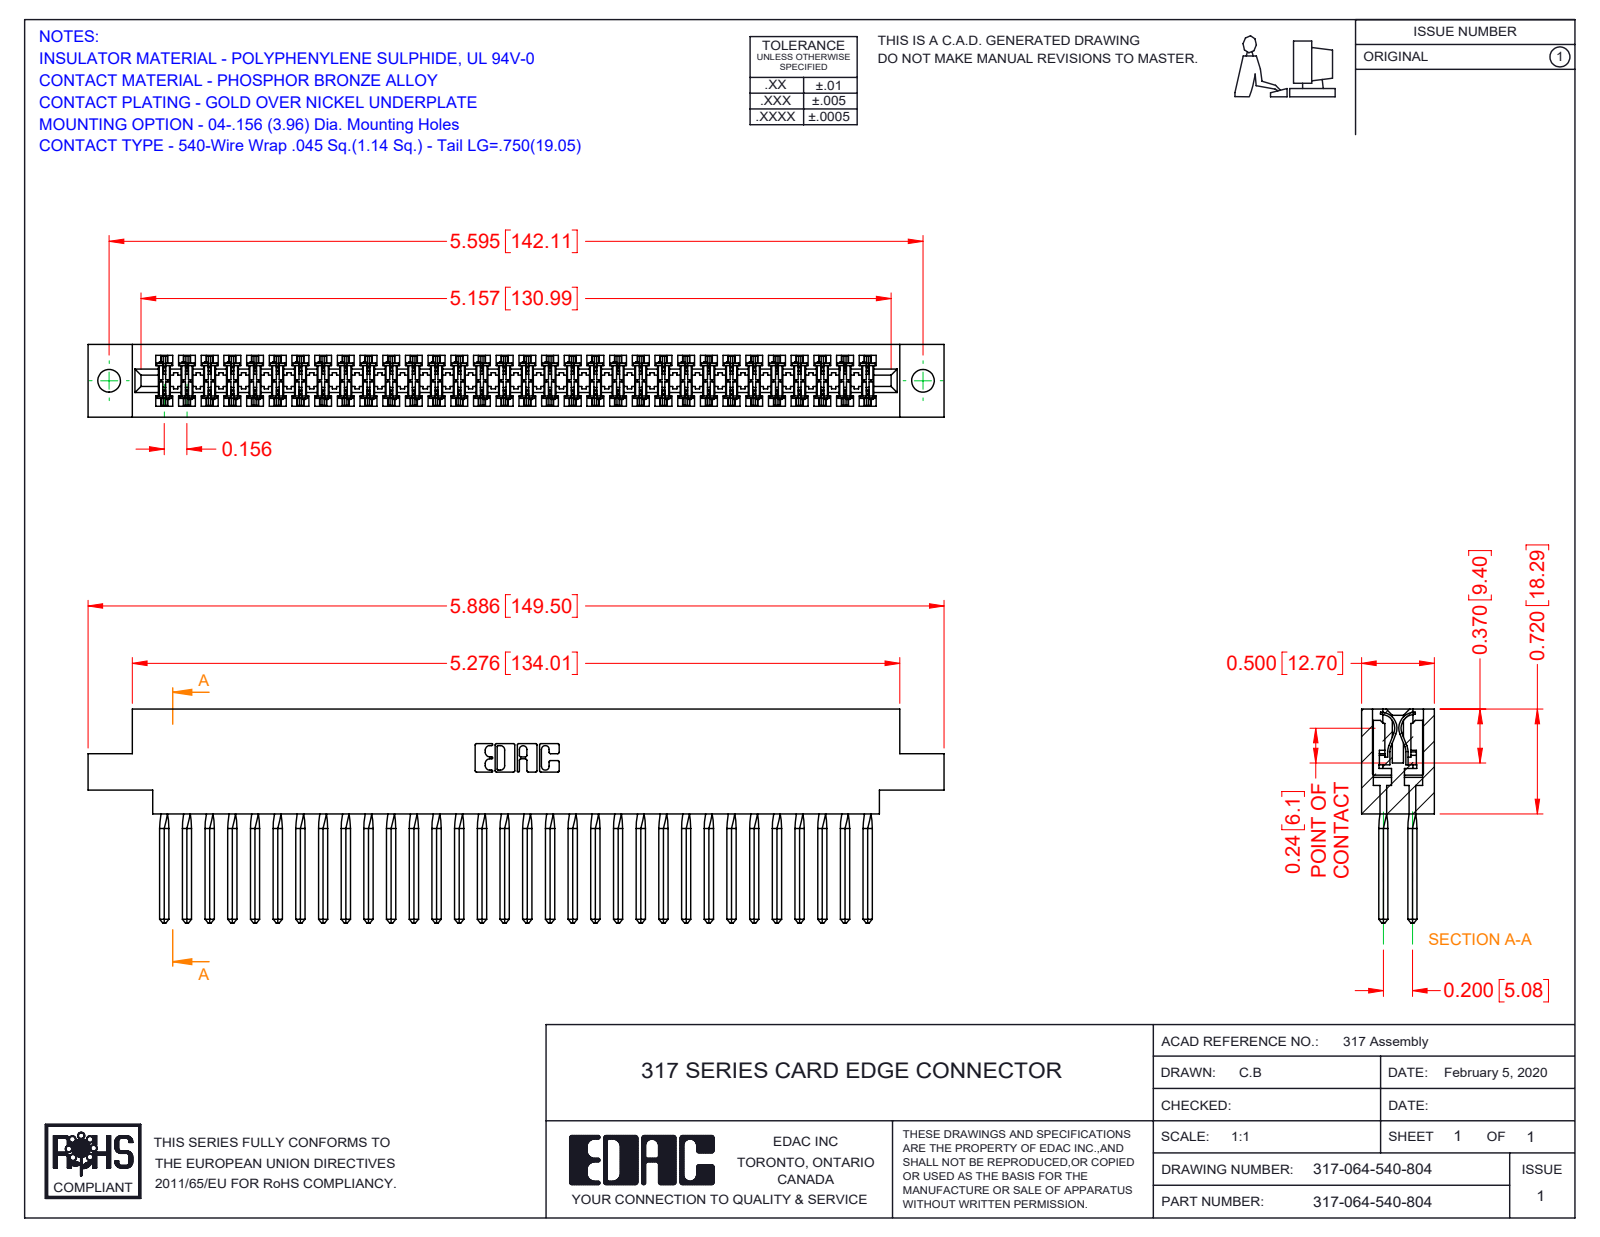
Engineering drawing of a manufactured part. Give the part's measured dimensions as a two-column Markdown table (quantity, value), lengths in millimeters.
| quantity | value |
| --- | --- |
| part name | 317 Part_.156 Dia - TH; 317-064-540-804; 317-290-001_540 |
| STEP written by | SolidWorks 2016 (CONFIG_CONTROL_DESIGN) |
| units | millimeters |
| bodies | 65 solids, 5798 faces (4730 planar, 812 cylindrical, 256 other) |
| overall size | 149.5 × 37.3 × 12.7 |
| volume | 24 660 mm³ |
| surface area | 36 220 mm² |
| round holes (diameter × count) | 4 × 2 |
| partial cylindrical surfaces (radius × count) | 0.4 × 128, 0.3 × 22, 0.2 × 6, 0.8 × 6, 0.7 × 3, 2.4 × 2, 2.5 × 2, 2.8 × 2 |
| main face-to-face distances | 12.7, 1.9, 10.8, 8.9, 2.8, 5, 2.4, 5.1, 2.9, 3.3 |
| hole center spacings | 142.1 |
